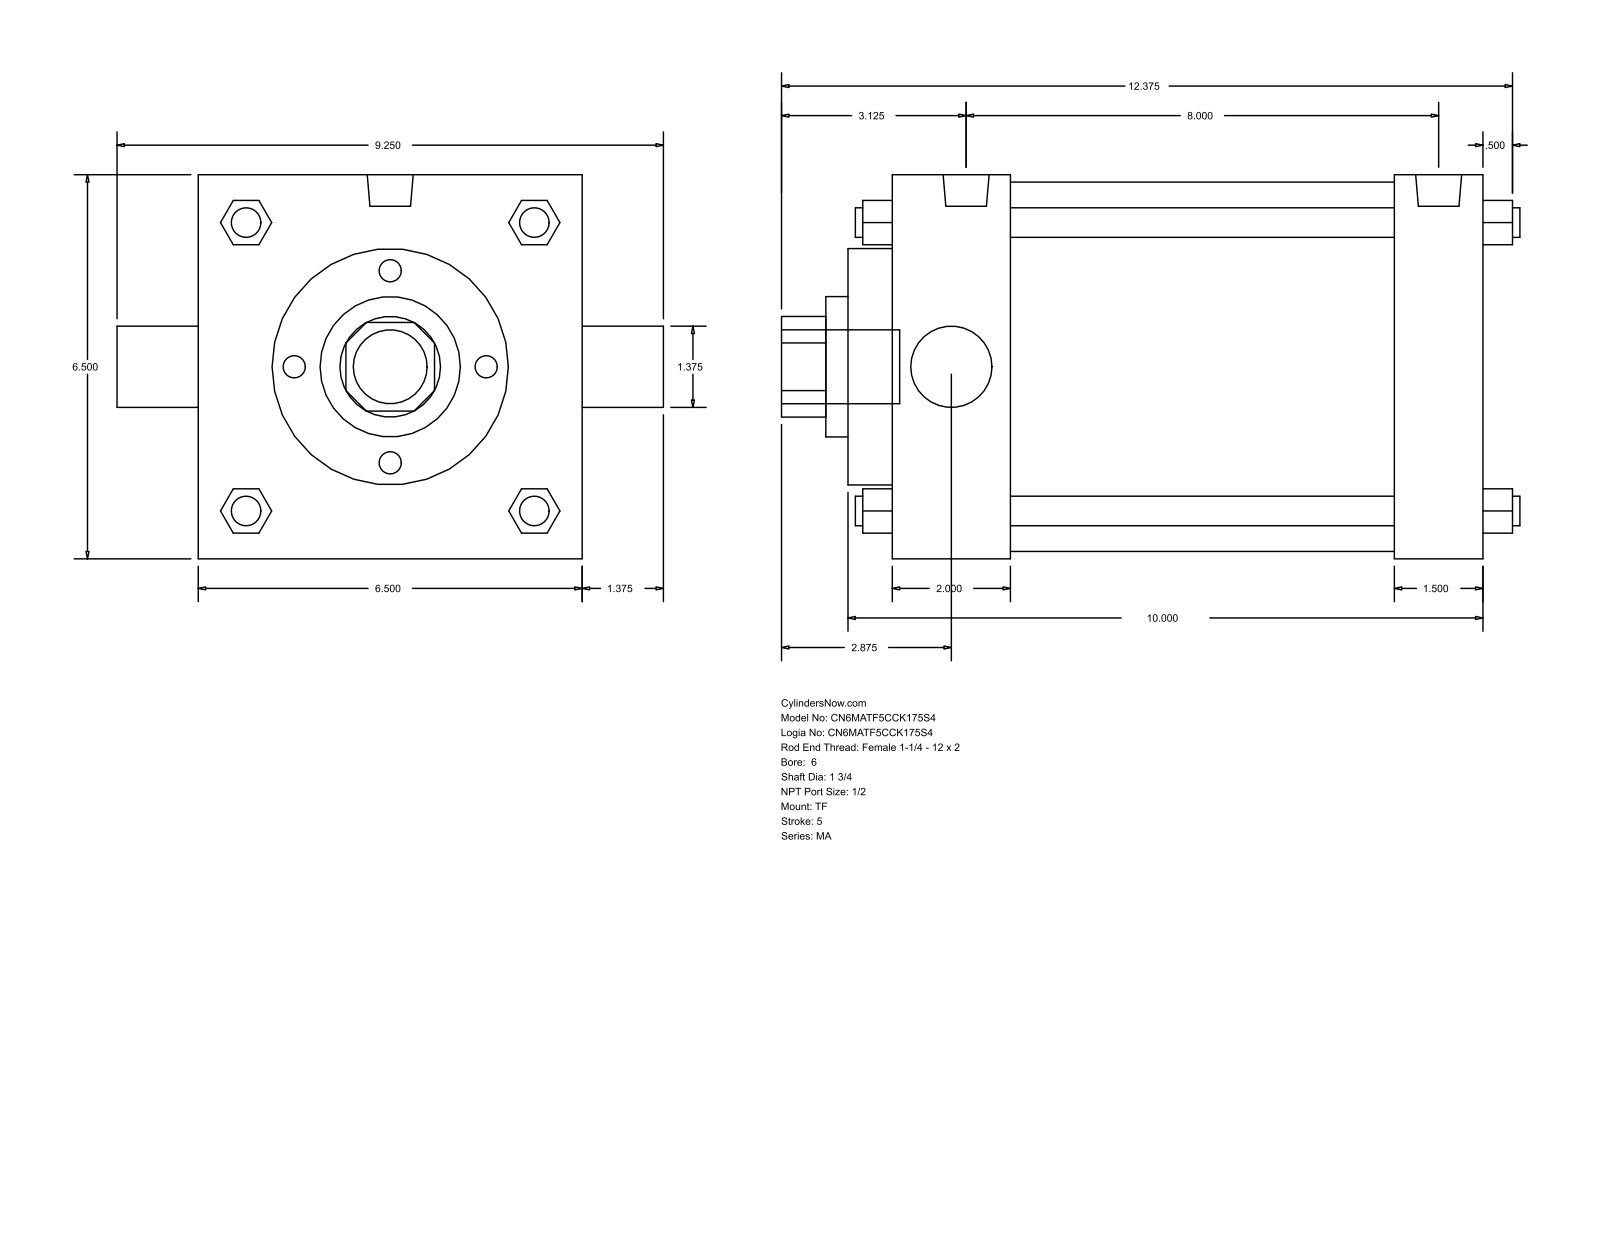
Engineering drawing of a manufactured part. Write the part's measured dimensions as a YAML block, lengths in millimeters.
part_name: "MA_TF__0600_1.75"
step_written_by: "GSSL Pune (CONFIG_CONTROL_DESIGN)"
units: millimeters
bodies: {solids: 0, faces: 122, planar: 93, cylindrical: 29, other: 0}
overall_size: [317.5, 234.95, 165.1]
round_holes:
  - {diameter: 34.92, count: 1}
  - {diameter: 44.45, count: 1}
  - {diameter: 60.33, count: 1}
  - {diameter: 101.6, count: 1}
  - {diameter: 158.75, count: 1}
round_bosses_or_shafts:
  - {diameter: 12.7, count: 4}
  - {diameter: 17.46, count: 3}
  - {diameter: 19.77, count: 2}
  - {diameter: 31.75, count: 1}
partial_cylinders:
  - {radius: 21.63, count: 1}
face_to_face_distances: [165.1, 254, 19.05, 50.8, 215.9, 38.1, 203.2, 69.85, 234.95, 273.05]
